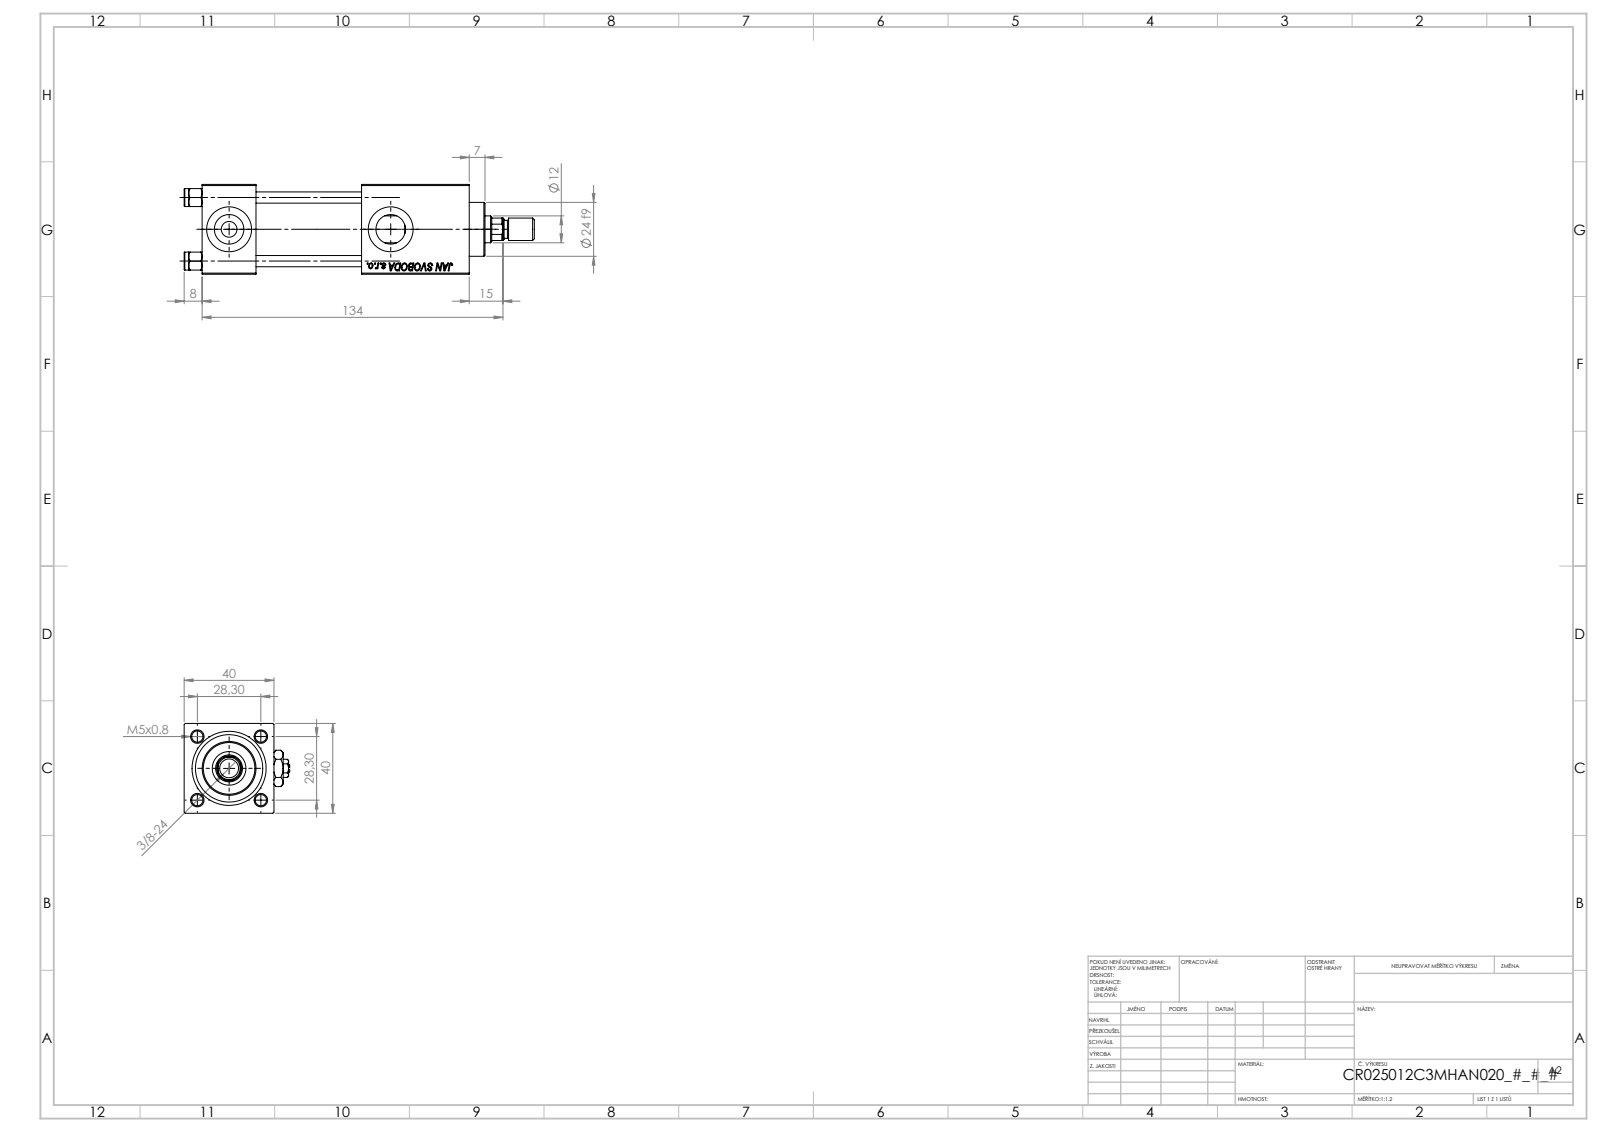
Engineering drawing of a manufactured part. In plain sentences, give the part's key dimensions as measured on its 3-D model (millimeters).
The part is named "Zatka_pro_OIL_PORT; ROD_END_AH; NUT_M5_C; V215CR_C_TYCINKA (+3 more)". Its 3-D file was written by "SolidWorks 2019 (CONFIG_CONTROL_DESIGN)". It is 14 solids with 1262 faces: 576 planar, 102 cylindrical and 584 other. Overall it measures 156 by 47 by 40 millimeters. Its volume is 142 017 cubic millimeters and its surface area 56 820 square millimeters. Round holes: 4 of diameter 5, 3 of diameter 20, 2 of diameter 7, 2 of diameter 13.16, 1 of diameter 6.5, 1 of diameter 12, 1 of diameter 15, 1 of diameter 25, 1 of diameter 30. Round bosses or shafts: 5 of diameter 8, 1 of diameter 31, 1 of diameter 24, 1 of diameter 10. Partial cylindrical surfaces (rounded edges, fillets, slot ends): 1 of radius 5.5. The main face-to-face distances are 40, 24, 39.8, 48, 90.3, 66.3, 71, 47, 19.3, 119. The hole center spacings are 20.01, 28.3, 40.02, 72.
